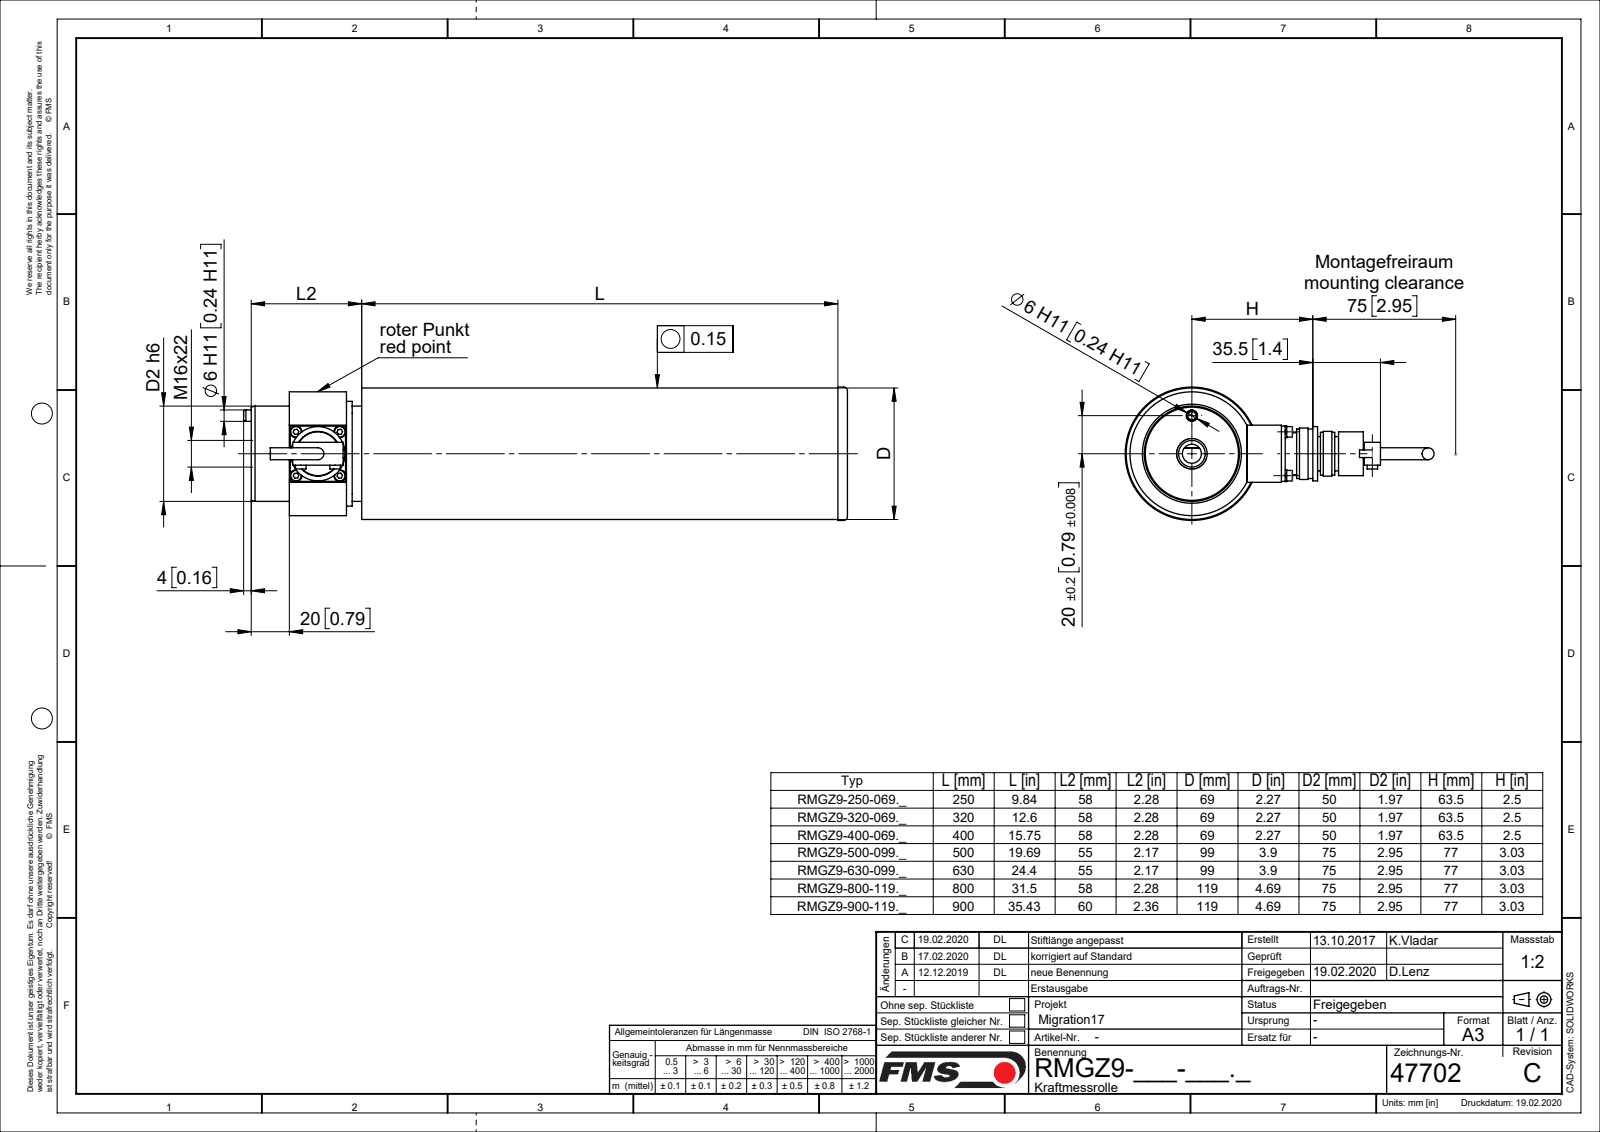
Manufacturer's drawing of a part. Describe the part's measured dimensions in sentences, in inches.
The part is named "ZEICHNUNG2; 47702_STP_A; 47726-04_STP_01; 49408_01 (+8 more)". Its 3-D file was written by "Mechanical Desktop 2009 (CONFIG_CONTROL_DESIGN)". It is 31 solids with 589 faces: 170 planar, 259 cylindrical and 160 other. Overall it measures 12.48 by 6.384 by 2.756 inches. Its volume is 38.42 cubic inches and its surface area 366.9 square inches. Round holes: 6 of diameter 0.098, 4 of diameter 0.122, 4 of diameter 0.134, 1 of diameter 0.13, 1 of diameter 0.236, 1 of diameter 0.394, 1 of diameter 0.472, 1 of diameter 0.551, 1 of diameter 0.669, 1 of diameter 0.866, 1 of diameter 0.906, 1 of diameter 1.024. Round bosses or shafts: 6 of diameter 0.217, 4 of diameter 0.244, 4 of diameter 0.118, 4 of diameter 0.098, 1 of diameter 2.756, 1 of diameter 2.717, 1 of diameter 2.559, 1 of diameter 2.283. Partial cylindrical surfaces (rounded edges, fillets, slot ends): 4 of radius 0.004, 4 of radius 0.433, 2 of radius 0.165, 2 of radius 0.167, 1 of radius 0.689, 1 of radius 0.874, 1 of radius 0.999. The main face-to-face distances are 1.969, 0.079, 0.118, 0.197, 1.378, 10.157, 0.787, 1.496, 3.268, 0.709. The hole center spacings are 0.64, 0.906, 0.978, 1.281, 0.714, 0.787, 1.007, 1.463.
